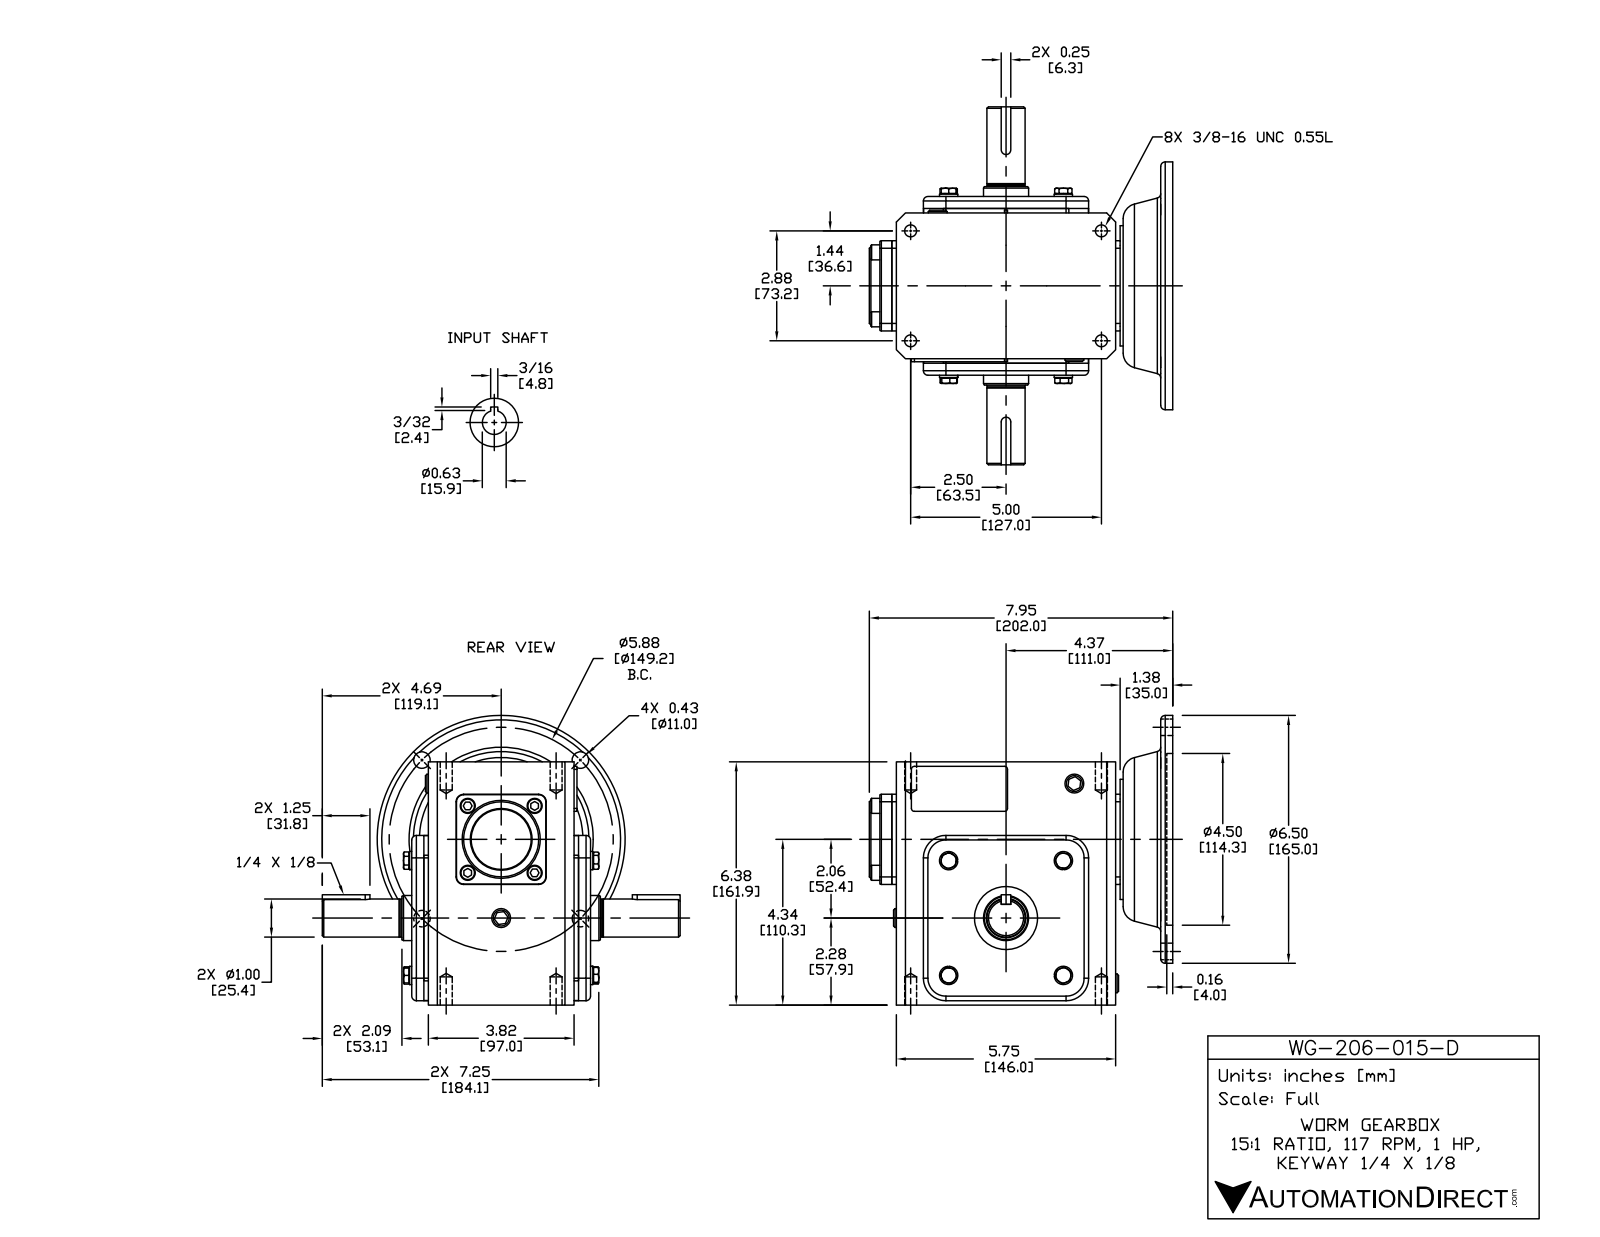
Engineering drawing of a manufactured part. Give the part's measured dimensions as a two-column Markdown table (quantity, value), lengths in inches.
| quantity | value |
| --- | --- |
| part name | WG-206-015-D |
| STEP written by | SolidWorks 2015 (CONFIG_CONTROL_DESIGN) |
| units | inches |
| bodies | 45 solids, 639 faces (311 planar, 194 cylindrical, 134 other) |
| overall size | 9.38 × 7.953 × 7.591 |
| volume | 174.7 in³ |
| surface area | 422.9 in² |
| round holes (diameter × count) | 0.313 × 4, 0.406 × 4, 0.591 × 1, 0.625 × 1, 1.181 × 1, 1.457 × 1, 1.654 × 1, 3.543 × 1, 4.5 × 1 |
| round bosses / shafts (diameter × count) | 0.394 × 8, 0.48 × 4, 6.496 × 1, 3.15 × 1, 2.047 × 1, 1.575 × 1, 1.181 × 1, 1.142 × 1 |
| partial cylindrical surfaces (radius × count) | 0.079 × 8, 0.118 × 8, 0.197 × 4, 0.591 × 4, 0.02 × 2, 0.039 × 2, 0.125 × 2, 2.717 × 1 |
| main face-to-face distances | 0.315, 0.118, 4.055, 0.433, 4.37, 4.252, 3.937, 6.375, 4.685, 0.709 |
| hole center spacings | 2.937, 4.154, 2.077, 2.88, 4.631, 5, 5.77, 5.875 |
